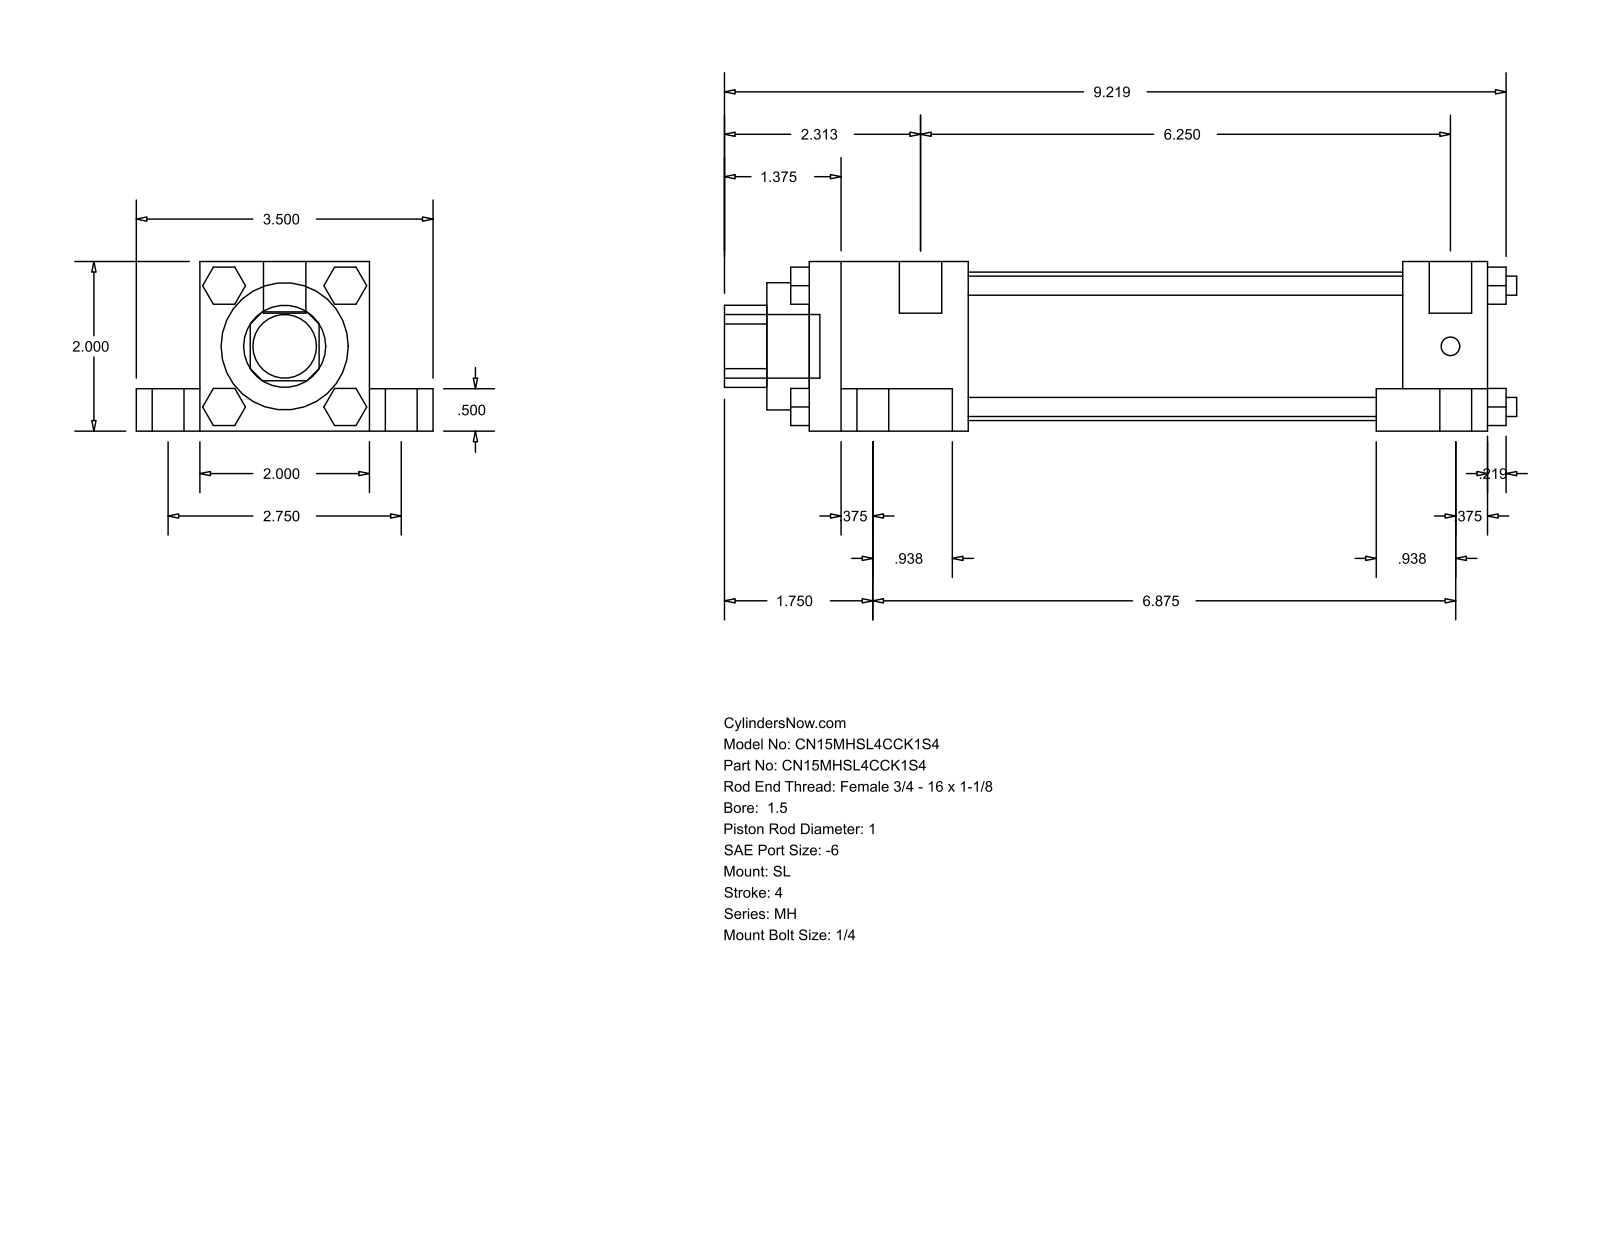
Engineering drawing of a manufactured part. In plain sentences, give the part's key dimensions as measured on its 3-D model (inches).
The part is named "MH_SL__0150_1". Its 3-D file was written by "GSSL Pune (CONFIG_CONTROL_DESIGN)". It is 0 solids with 148 faces: 112 planar, 36 cylindrical and 0 other. Overall it measures 9.344 by 3.5 by 2 inches. Round holes: 1 of diameter 1, 1 of diameter 1.5, 1 of diameter 1.75. Round bosses or shafts: 4 of diameter 0.625, 4 of diameter 0.375, 4 of diameter 0.225, 4 of diameter 0.219, 2 of diameter 0.5, 1 of diameter 0.75. Partial cylindrical surfaces (rounded edges, fillets, slot ends): 1 of radius 0.484. The main face-to-face distances are 2, 0.5, 1.5, 0.75, 2.75, 8, 1, 0.375, 1.313, 6.313.
